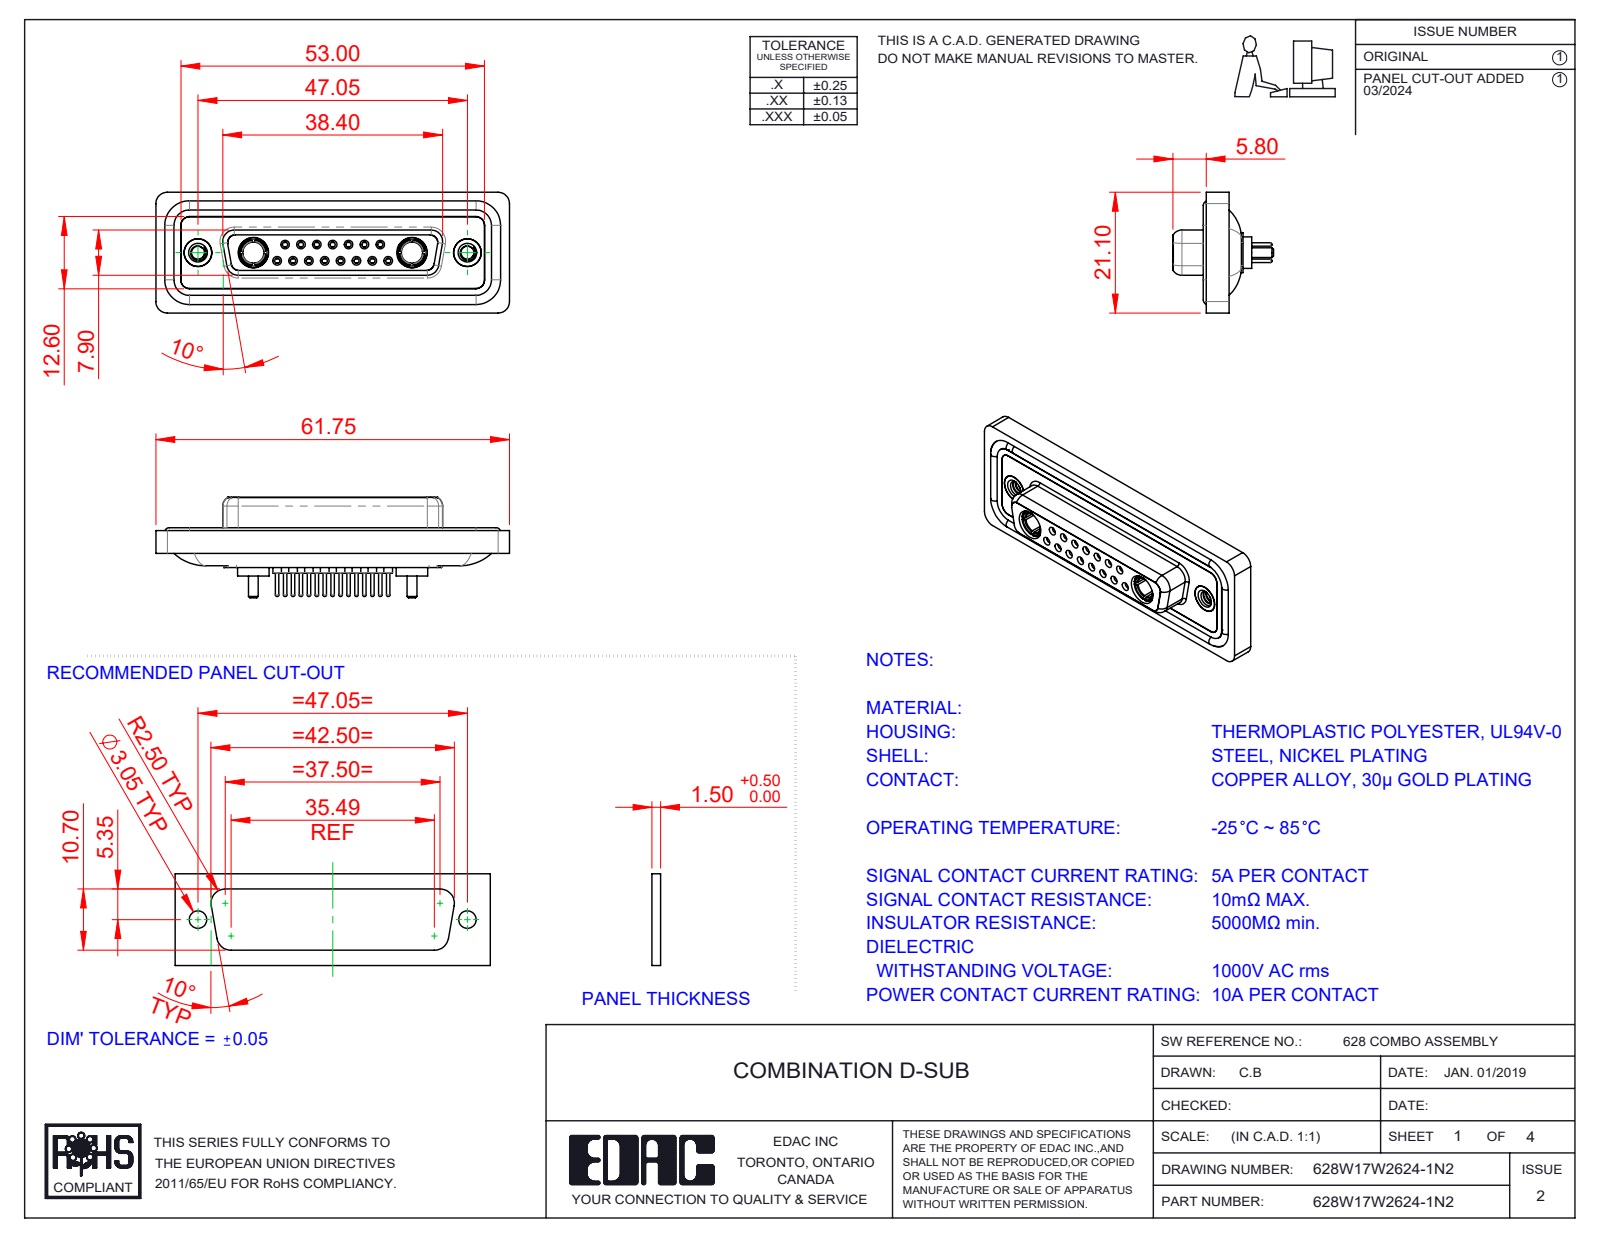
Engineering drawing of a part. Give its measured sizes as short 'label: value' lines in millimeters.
name: 628Combo Shell Rear_25 Contacts; 628Combo Threaded Rivet_2; Power Socket_10A S; 628Combo Shell Front_25 Contacts (+5 more)
written by: SolidWorks 2023 (CONFIG_CONTROL_DESIGN)
unit: mm
bodies: 26 solids, 1359 faces (388 planar, 519 cylindrical, 452 other)
size: 61.75 × 21.1 × 17.55
volume: 8 295 mm³; area: 13 830 mm²
holes: 15× ⌀0.9, 15× ⌀1.1, 15× ⌀1.5, 15× ⌀2, 8× ⌀1.6, 7× ⌀1.7, 4× ⌀4.85, 2× ⌀2.26, 2× ⌀3.7, 2× ⌀4, 2× ⌀4.05, 2× ⌀5
bosses: 15× ⌀2.2, 15× ⌀0.6, 11× ⌀1.6, 2× ⌀5.5, 2× ⌀5.2, 2× ⌀4.96, 2× ⌀4.95, 2× ⌀4.8
rounds: 22× R1.5, 18× R2, 8× R1.35, 8× R1.6, 4× R0.25, 4× R0.5, 4× R0.6, 4× R0.65
face distances: 0.4, 1.8, 7.45, 5.65, 6.6, 0.5, 7.05, 1.6, 2.9, 1.1
hole spacings: 3.16, 2.77, 8.31, 5.54, 5.03, 5.04, 7.49, 11.08
